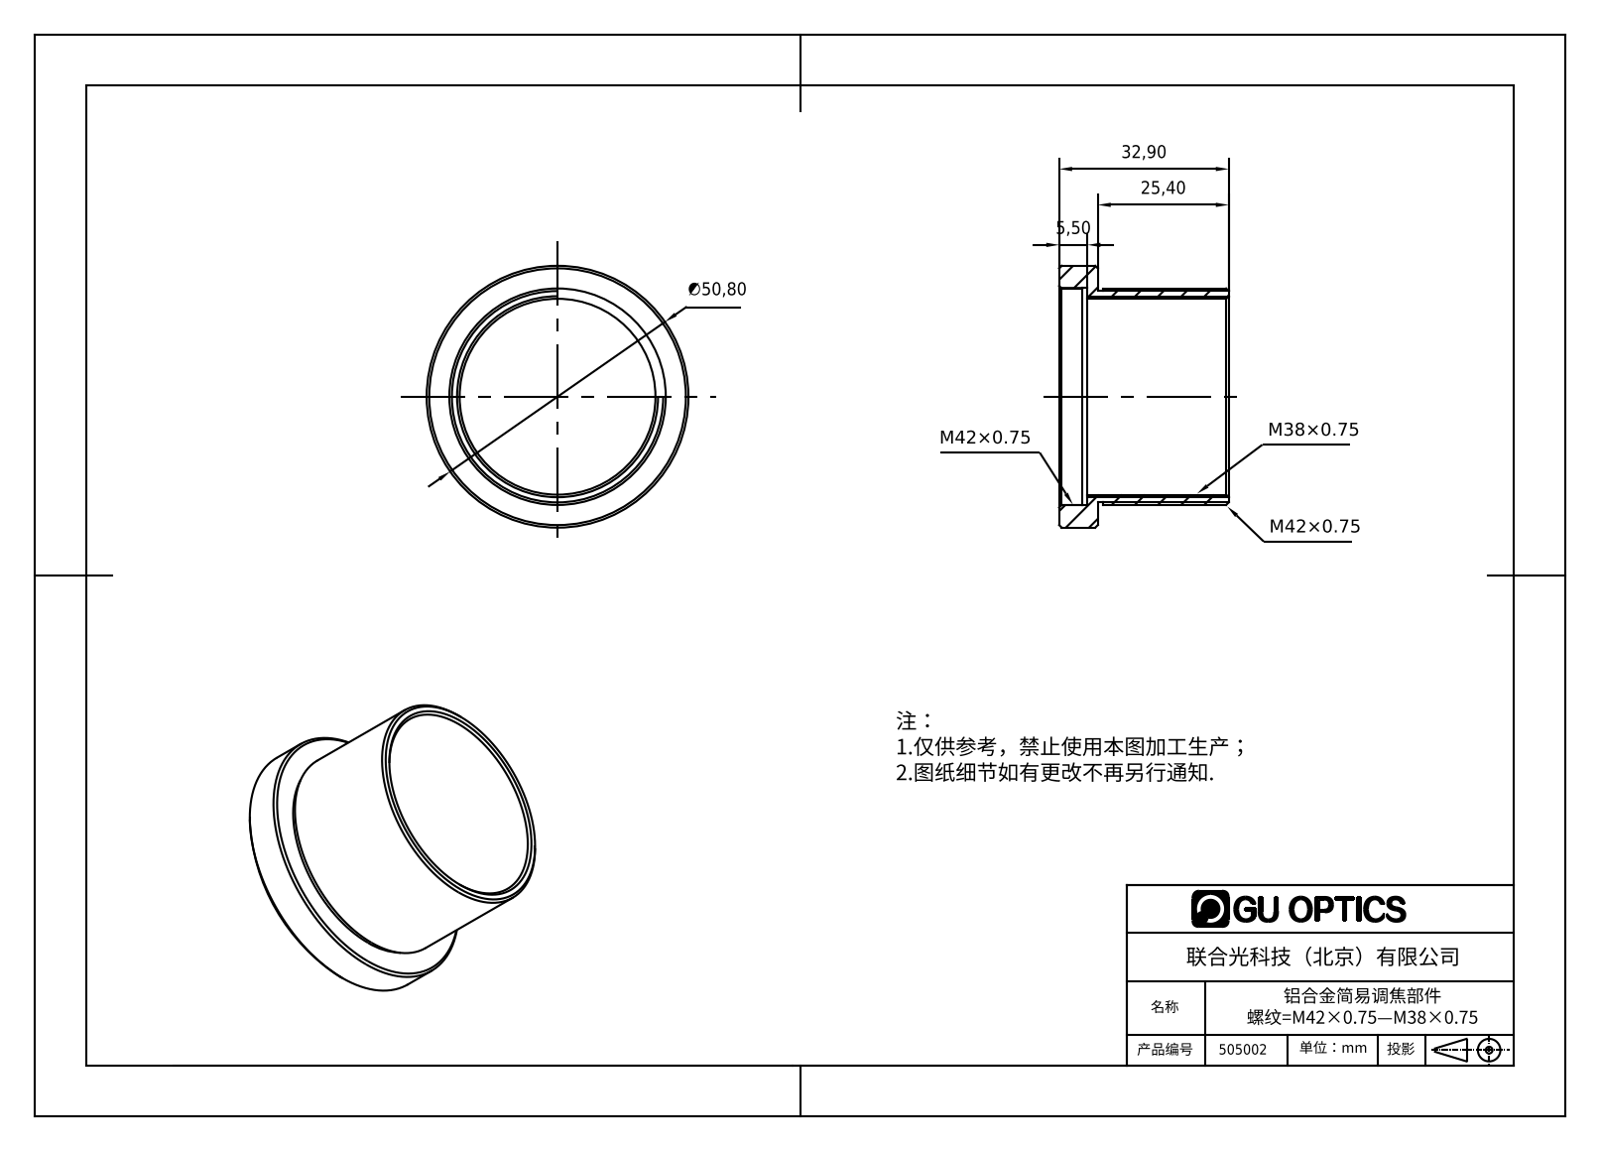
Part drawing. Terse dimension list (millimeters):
name: 505002
written by: SolidWorks 2016 (CONFIG_CONTROL_DESIGN)
unit: mm
bodies: 1 solid, 28 faces (6 planar, 12 cylindrical, 10 other)
size: 50.8 × 50.8 × 32.9
volume: 11 531 mm³; area: 10 279 mm²
holes: 1× ⌀38, 1× ⌀42, 1× ⌀42.2
bosses: 1× ⌀50.8, 1× ⌀41
face distances: 7.5, 5.5, 2, 32.9, 27.4, 25.4, 1, 3, 8.5, 24.4
